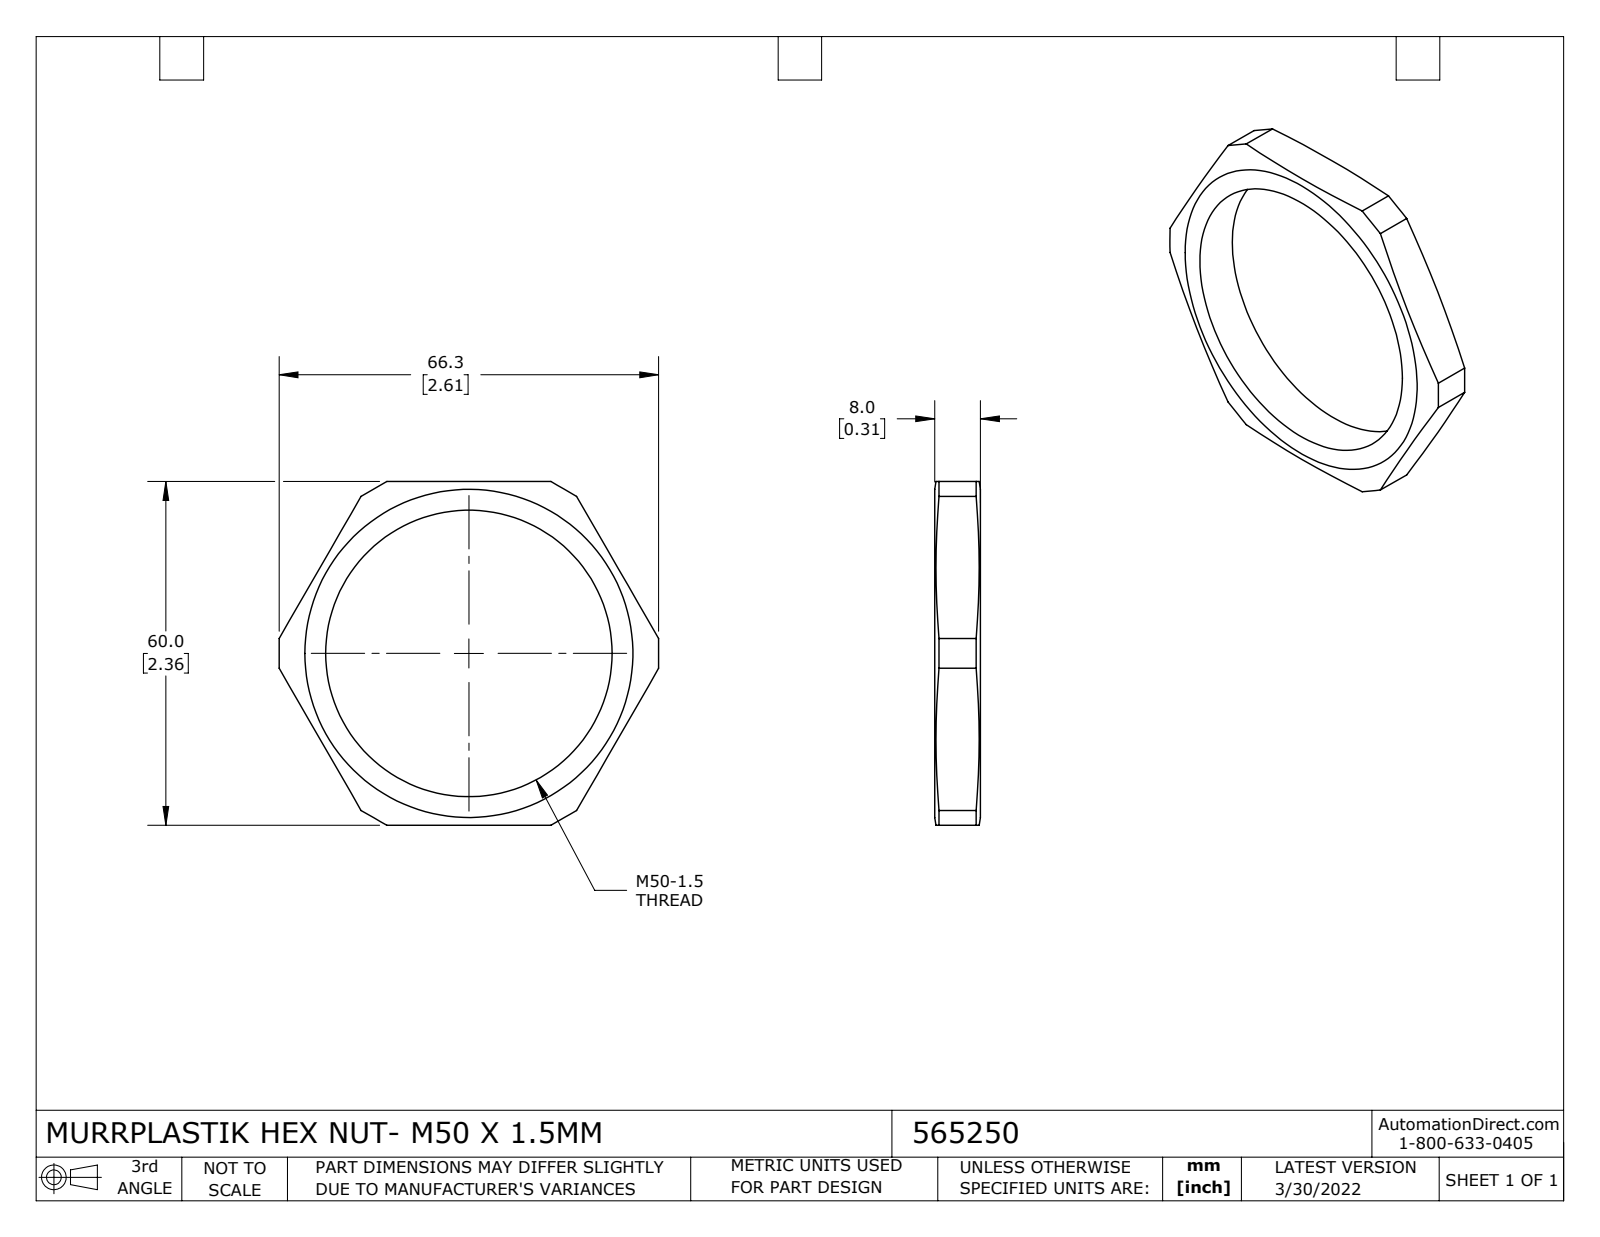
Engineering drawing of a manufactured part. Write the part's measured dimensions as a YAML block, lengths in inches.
part_name: "565250"
step_written_by: "SolidWorks 2021 (CONFIG_CONTROL_DESIGN)"
units: inches
bodies: {solids: 1, faces: 20, planar: 14, cylindrical: 2, other: 4}
overall_size: [2.61, 2.362, 0.315]
volume: 0.535
surface_area: 7.701
round_holes:
  - {diameter: 1.969, count: 1}
face_to_face_distances: [2.362, 0.315, 2.609]
